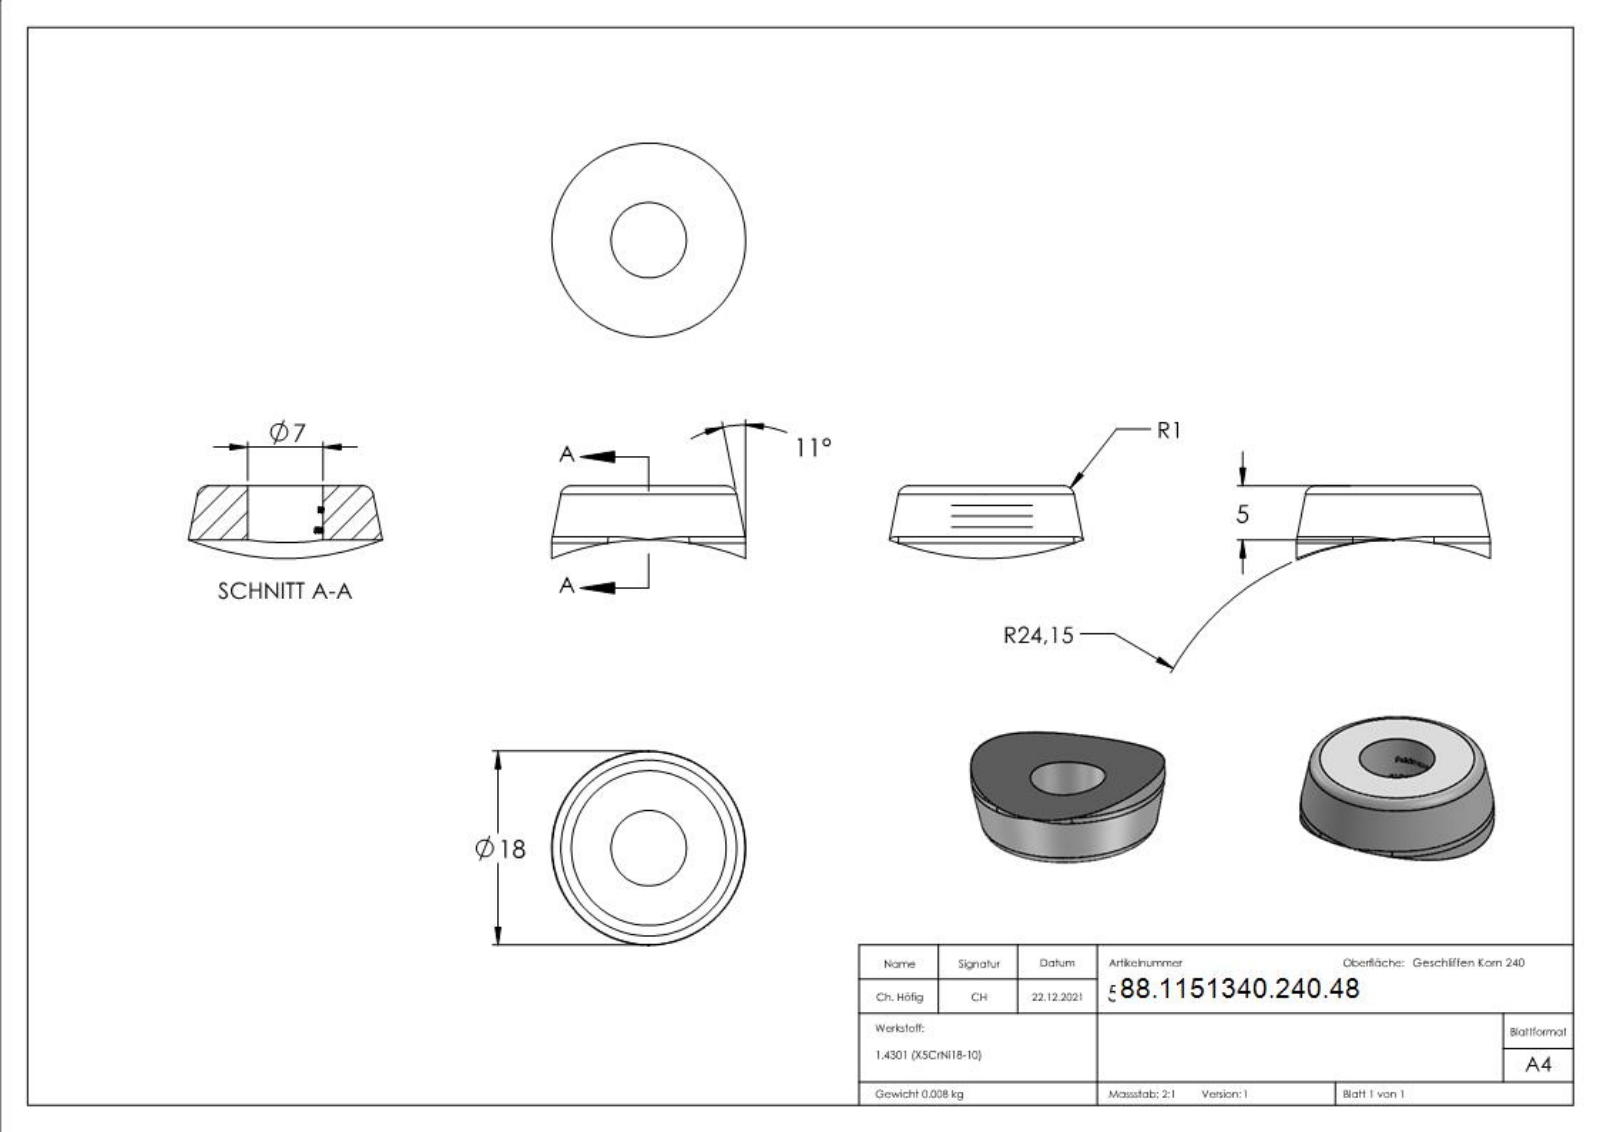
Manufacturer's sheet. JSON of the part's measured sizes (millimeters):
{"part_name": "51340-240-48", "step_written_by": "SolidWorks 2018 (CONFIG_CONTROL_DESIGN)", "units": "millimeters", "bodies": {"solids": 1, "faces": 280, "planar": 123, "cylindrical": 35, "other": 122}, "overall_size": [18, 18, 6.74], "volume_mm3": 1043, "surface_area_mm2": 808, "round_holes": [[7, 1]], "partial_cylinders_radius": [[3.6, 1], [9, 1], [24.15, 1]], "face_to_face_distances": [1.59, 1.88, 2.14, 1.94, 0.35, 1.64, 2.18, 1.47, 4.21, 0.88]}
